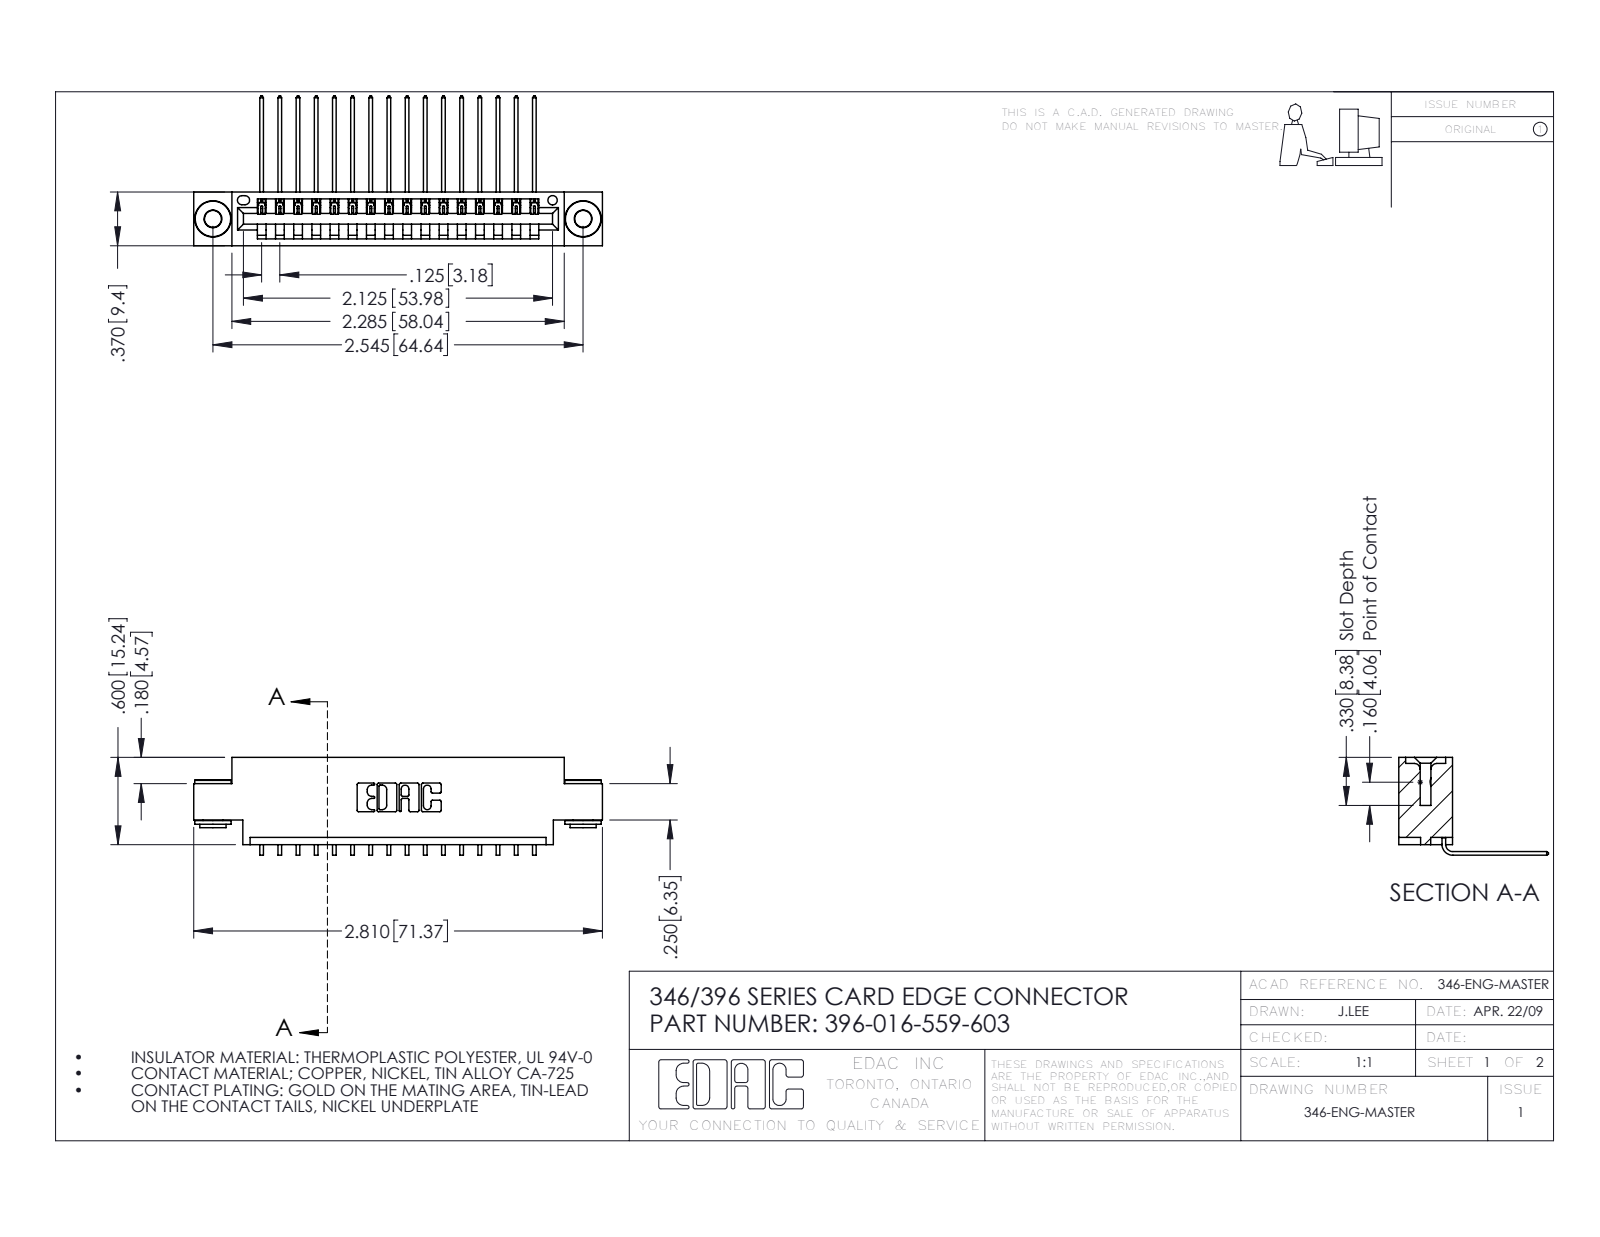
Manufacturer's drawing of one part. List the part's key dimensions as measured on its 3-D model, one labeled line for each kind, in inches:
Part name (STEP PRODUCT): 396-016-559-603; 345-292-001_558 559 Tail - 1; 345-250-002_345-250-002-102; 346 Part_0.170 Offset - 0.156 Dia-TH
STEP written by: SolidWorks 2016 (CONFIG_CONTROL_DESIGN)
Units: inches
Bodies: 19 solids, 1124 faces (762 planar, 354 cylindrical, 8 other)
Overall size (bounding box): 2.81 × 1.03 × 0.673
Volume: 0.401 in³ · Surface area: 13.38 in²
Round holes (diameter × count): ⌀0.116 ×2, ⌀0.156 ×2, ⌀0.064 ×1
Round bosses / shafts (diameter × count): ⌀0.25 ×2, ⌀0.18 ×2, ⌀0.136 ×2
Partial cylindrical surfaces — rounded edges, fillets, slot ends (radius × count): R0.006 ×32, R0.01 ×22, R0.007 ×6, R0.031 ×6, R0.026 ×3, R0.031 ×2, R0.04 ×2, R0.014 ×1
Main face-to-face distances: 0.048, 0.37, 0.322, 0.25, 0.025, 0.072, 0.148, 0.222, 0.1, 0.174
Hole centre spacings: 0.246, 2.338, 2.545
